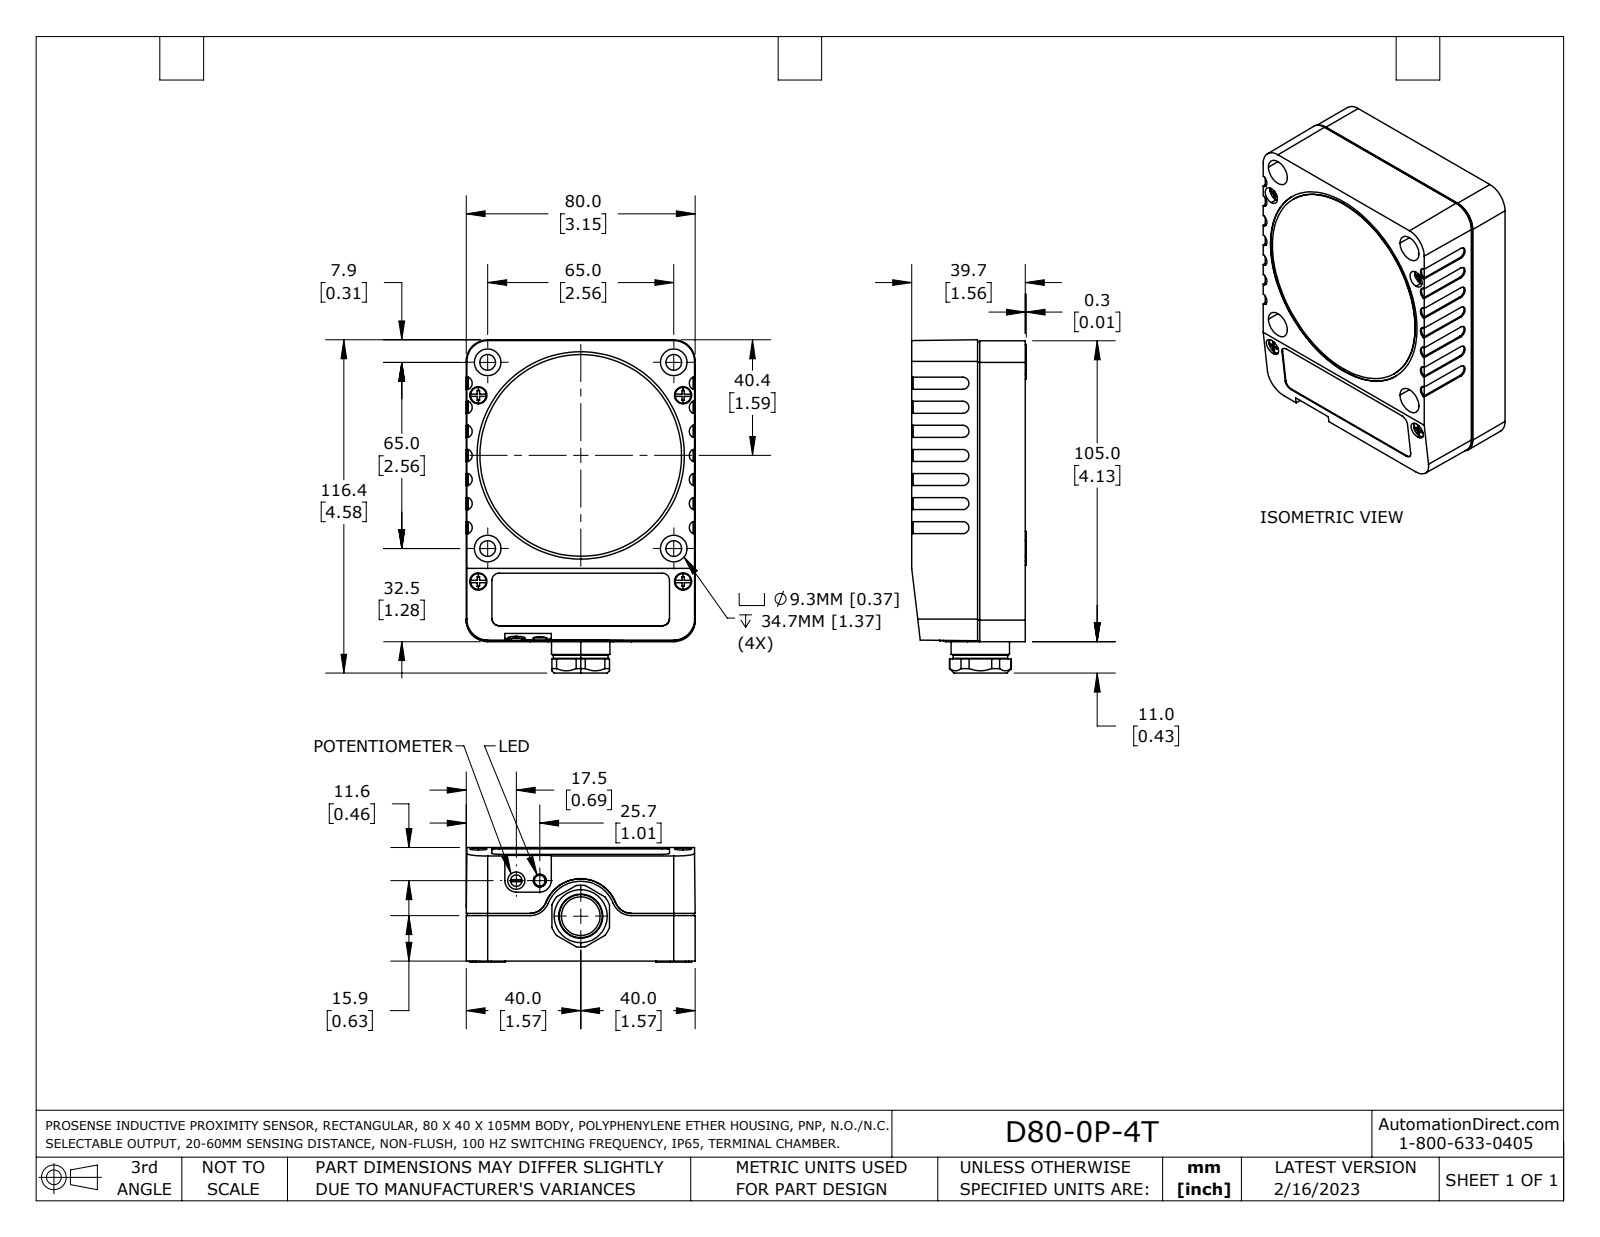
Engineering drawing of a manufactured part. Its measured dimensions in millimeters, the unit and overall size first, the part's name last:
Units: millimetres
Overall size (bounding box): 116.4 × 80 × 40
Round holes (diameter × count): ⌀3.2 ×4, ⌀5.5 ×4, ⌀5.8 ×4, ⌀6 ×4, ⌀9.3 ×4, ⌀9.4 ×4, ⌀13.5 ×1, ⌀15 ×1
Round bosses / shafts (diameter × count): ⌀5.6 ×4, ⌀5.5 ×4, ⌀72.4 ×1, ⌀70.4 ×1, ⌀20.4 ×1, ⌀19.1 ×1, ⌀6 ×1, ⌀4 ×1
Partial cylindrical surfaces — rounded edges, fillets, slot ends (radius × count): R2.3 ×14, R6 ×8, R2.1 ×7, R4 ×6, R1 ×4, R2.5 ×4, R7.2 ×4, R7.5 ×4
Main face-to-face distances: 39.7, 1.5, 78.5, 15.2, 24.5, 103.5, 0.5, 1.2, 80, 105
Hole centre spacings: 65, 11.9, 69.2, 53.6, 71.5, 76.6, 86.7, 91.9
Volume: 283 800 mm³ · Surface area: 51 960 mm²
Bodies: 1 solid, 515 faces (258 planar, 195 cylindrical, 62 other)
Part name (STEP PRODUCT): D80-0P-4T
STEP written by: SolidWorks 2021 (AUTOMOTIVE_DESIGN)
